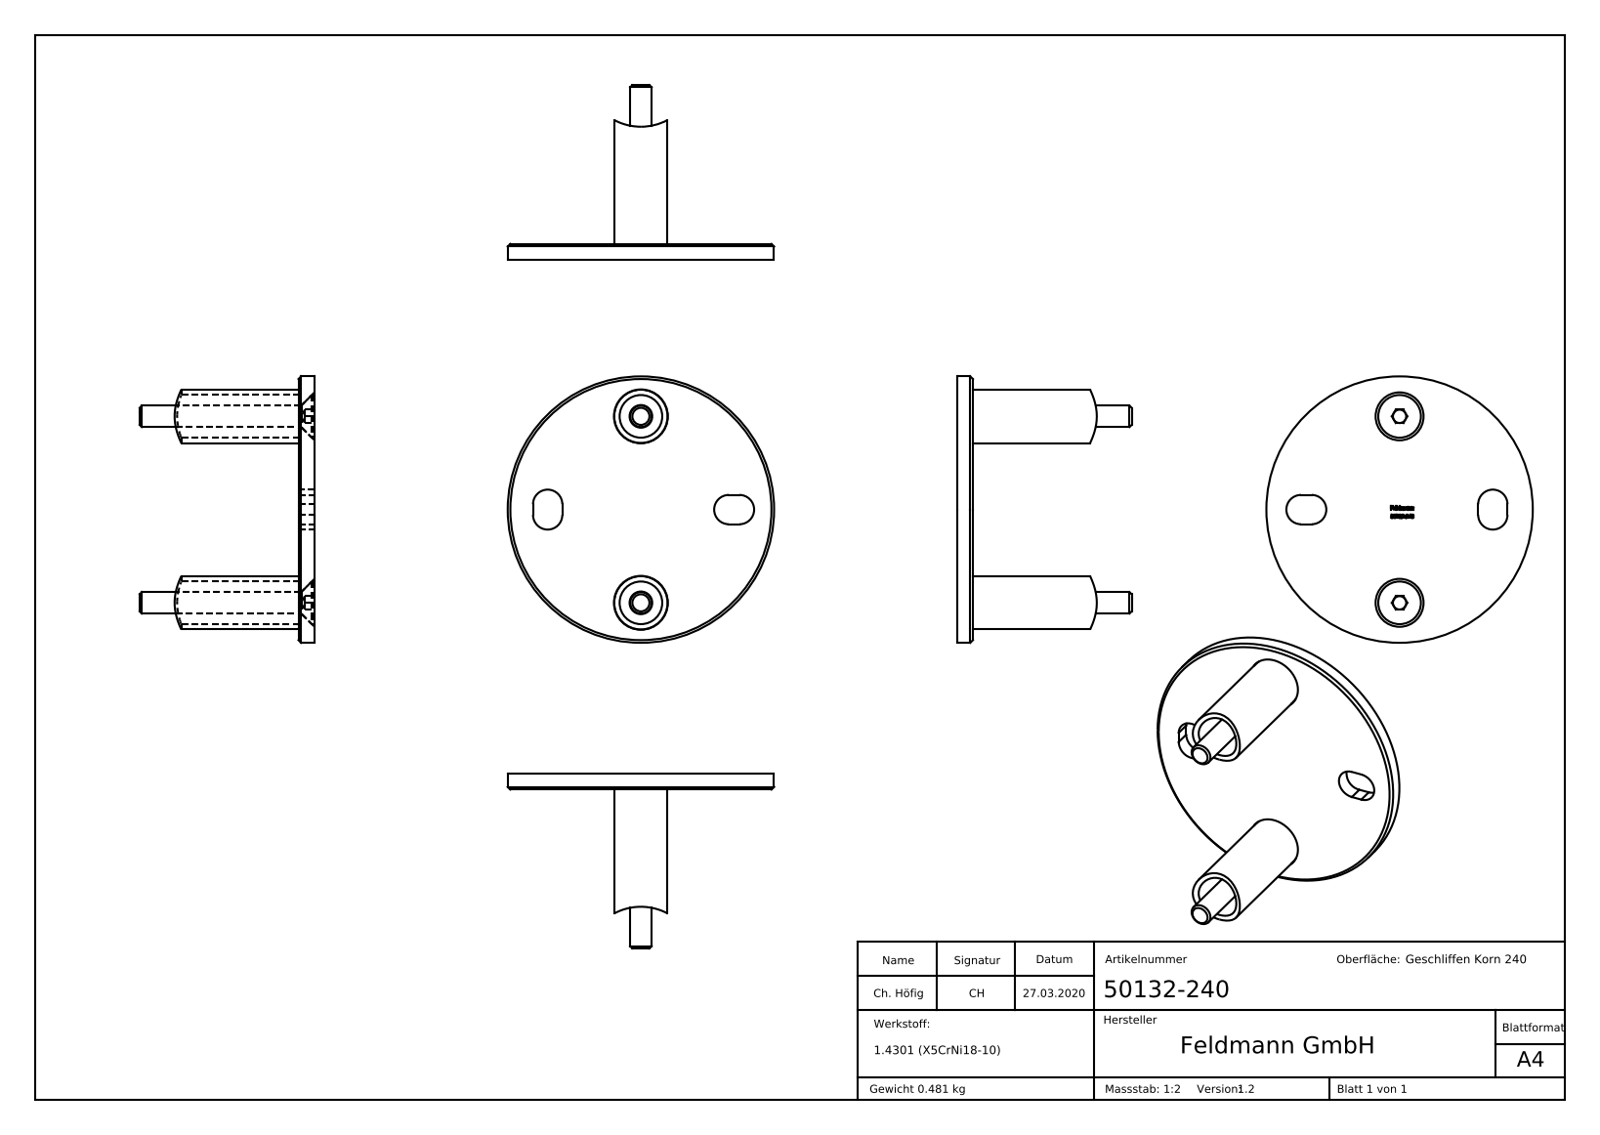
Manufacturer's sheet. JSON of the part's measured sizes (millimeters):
{"part_name": "50132-240 Teil2; DIN7991 M8x65_DIN7991 M8x65; 50132-240 Teil1_50132-240 Teil1; 50132-240 Teil1 (+3 more)", "step_written_by": "SolidWorks 2015 (CONFIG_CONTROL_DESIGN)", "units": "millimeters", "bodies": {"solids": 5, "faces": 287, "planar": 159, "cylindrical": 19, "other": 109}, "overall_size": [65000.6, 8000.02, 8000], "volume_mm3": 60848, "surface_area_mm2": 32276, "round_holes": [[8.5, 2], [16, 2], [20.2, 2]], "round_bosses_or_shafts": [[20, 2], [8, 2], [100, 1]], "partial_cylinders_radius": [[5.5, 4], [21.2, 1]], "face_to_face_distances": [6, 0.5, 5.5, 5.4, 4.9, 0.6, 65, 65.6, 60.1, 59.6], "hole_center_spacings": [70]}
